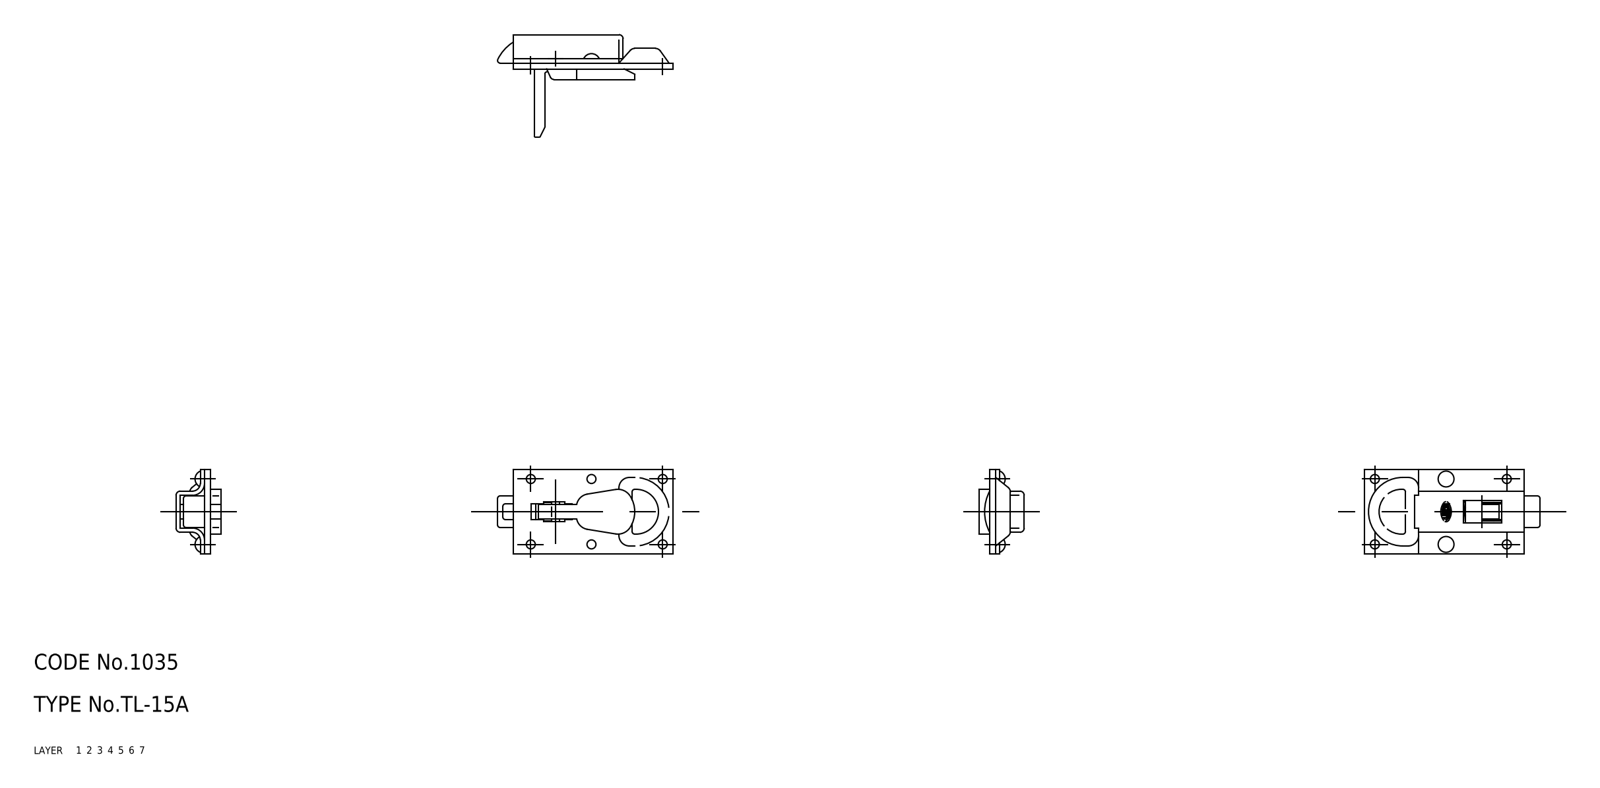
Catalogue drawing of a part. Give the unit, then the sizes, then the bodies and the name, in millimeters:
Units: millimetres
Overall size (bounding box): 33.3 × 16 × 8.5
Volume: 1 337 mm³ · Surface area: 2 932 mm²
Bodies: 7 solids, 200 faces (0 planar, 0 cylindrical, 200 other)
Part name (STEP PRODUCT): rivet; shaft; lever; latch (+3 more)
STEP written by: CADfix (AUTOMOTIVE_DESIGN)
